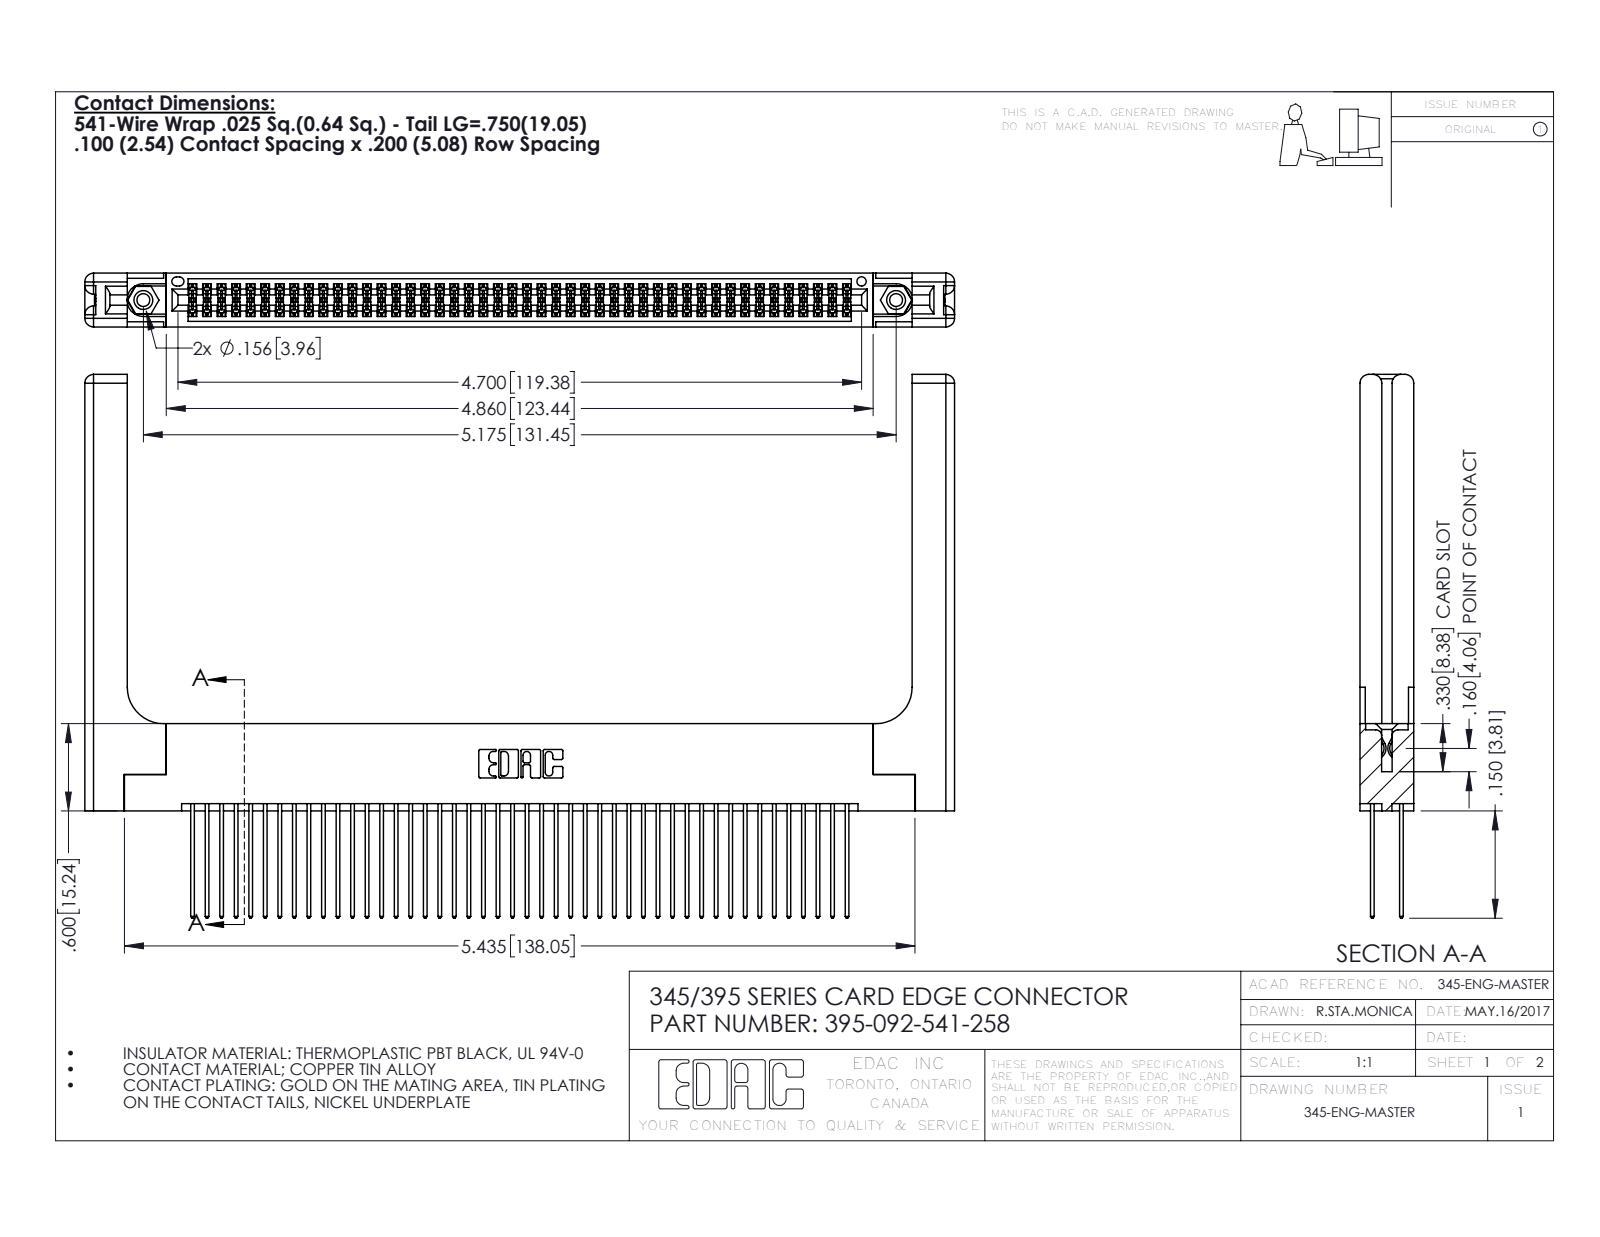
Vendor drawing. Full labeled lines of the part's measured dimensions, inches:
Part name (STEP PRODUCT): 345 Part_Flush Mounting Lugs - 0.156 Dia-TH; 345-220-058_345-220-058; 395-092-541-258; 345-250-001_345-250-001-102 (+1 more)
STEP written by: SolidWorks 2016 (CONFIG_CONTROL_DESIGN)
Units: inches
Bodies: 97 solids, 4982 faces (3264 planar, 1658 cylindrical, 60 other)
Overall size (bounding box): 5.979 × 3.737 × 0.37
Volume: 1.452 in³ · Surface area: 46.9 in²
Round holes (diameter × count): ⌀0.089 ×2, ⌀0.125 ×2, ⌀0.156 ×2, ⌀0.064 ×1
Round bosses / shafts (diameter × count): ⌀0.155 ×2
Partial cylindrical surfaces — rounded edges, fillets, slot ends (radius × count): R0.006 ×138, R0.01 ×92, R0.01 ×22, R0.06 ×16, R0.007 ×6, R0.031 ×6, R0.026 ×3, R0.014 ×2
Main face-to-face distances: 0.072, 0.298, 0.2, 0.37, 0.098, 0.272, 0.025, 0.225, 0.175, 0.148
Hole centre spacings: 0.27, 4.939, 5.175
